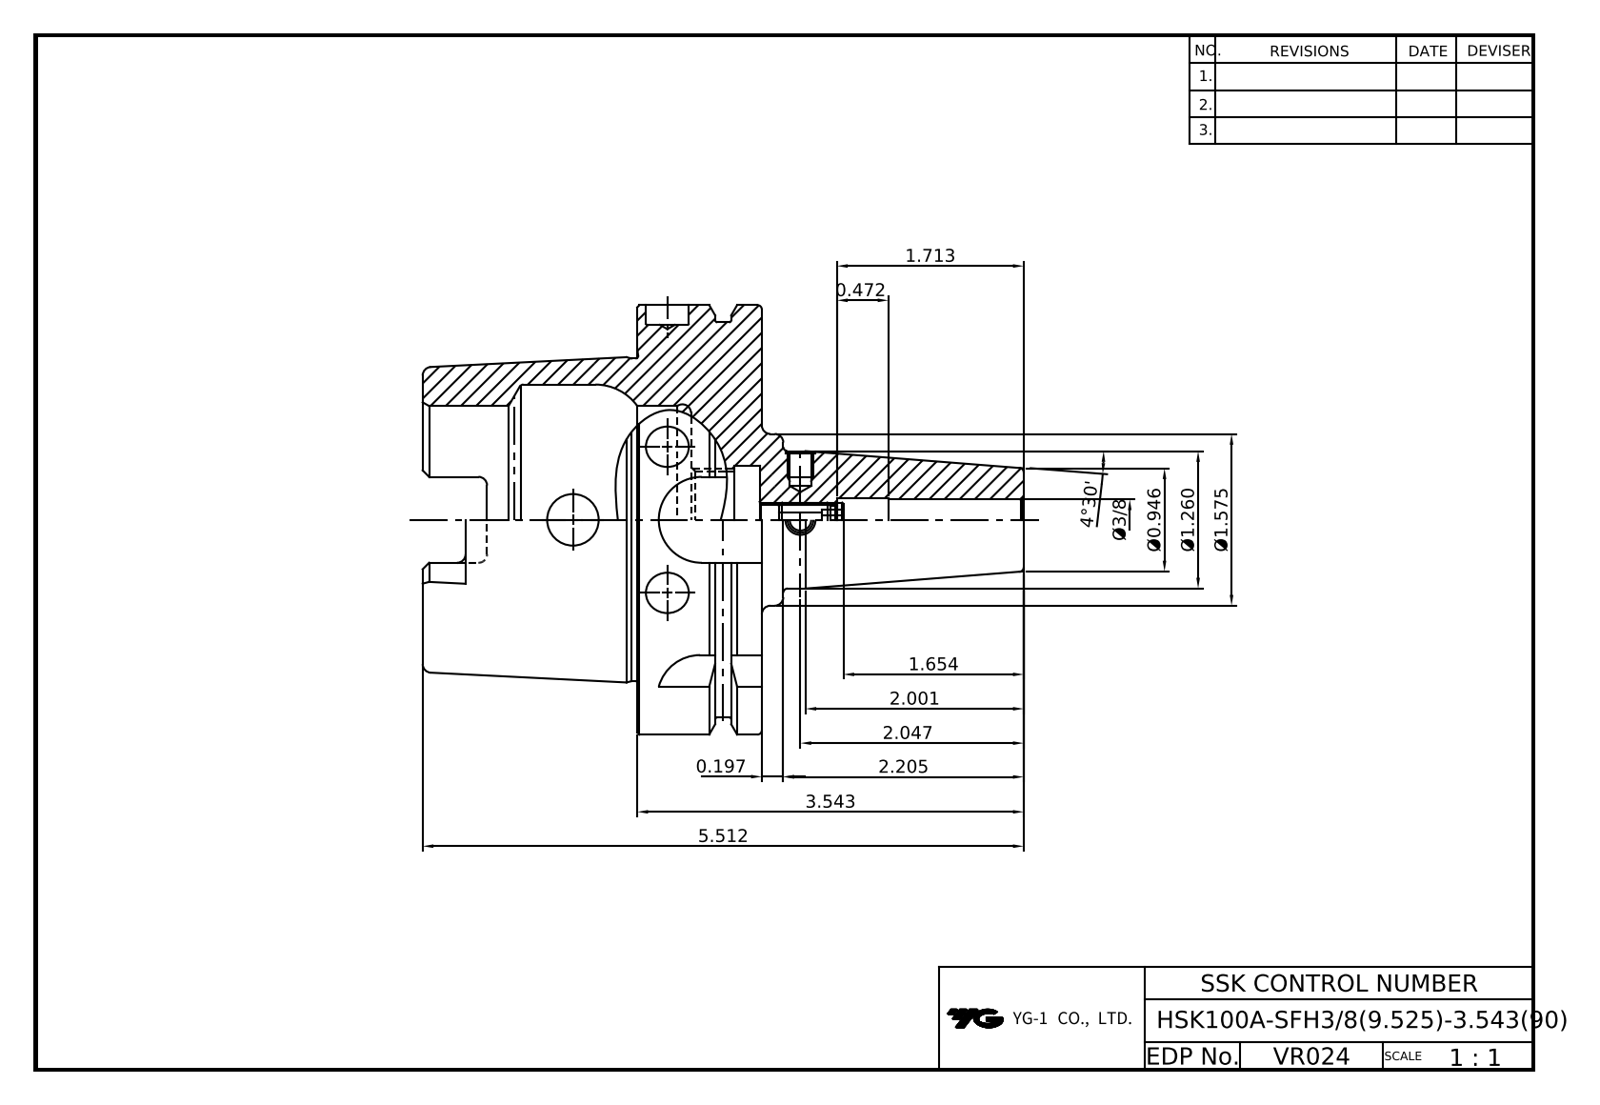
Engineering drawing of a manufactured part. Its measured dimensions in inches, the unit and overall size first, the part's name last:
Units: inches
Overall size (bounding box): 5.512 × 3.937 × 3.937
Round holes (diameter × count): ⌀0.276 ×3, ⌀0.197 ×2, ⌀0.236 ×2, ⌀0.315 ×1, ⌀0.375 ×1, ⌀0.394 ×1, ⌀0.402 ×1, ⌀0.472 ×1, ⌀0.886 ×1, ⌀0.945 ×1, ⌀0.984 ×1, ⌀2.087 ×1
Round bosses / shafts (diameter × count): ⌀3.937 ×1, ⌀3.622 ×1, ⌀2.959 ×1, ⌀1.575 ×1
Partial cylindrical surfaces — rounded edges, fillets, slot ends (radius × count): R0.079 ×6, R0.192 ×4, R0.394 ×4, R0.63 ×1
Main face-to-face distances: 1.142, 0.492, 0.65, 2.461, 1.969, 3.11, 0.394, 2.83, 2.682, 2.854
Hole centre spacings: 1.22, 2.087
Volume: 17.63 in³ · Surface area: 91.67 in²
Bodies: 1 solid, 216 faces (60 planar, 80 cylindrical, 76 other)
Part name (STEP PRODUCT): HSK100A-SFH9_525-90
STEP written by: CREO PARAMETRIC BY PTC INC, 2018400 (CONFIG_CONTROL_DESIGN)
